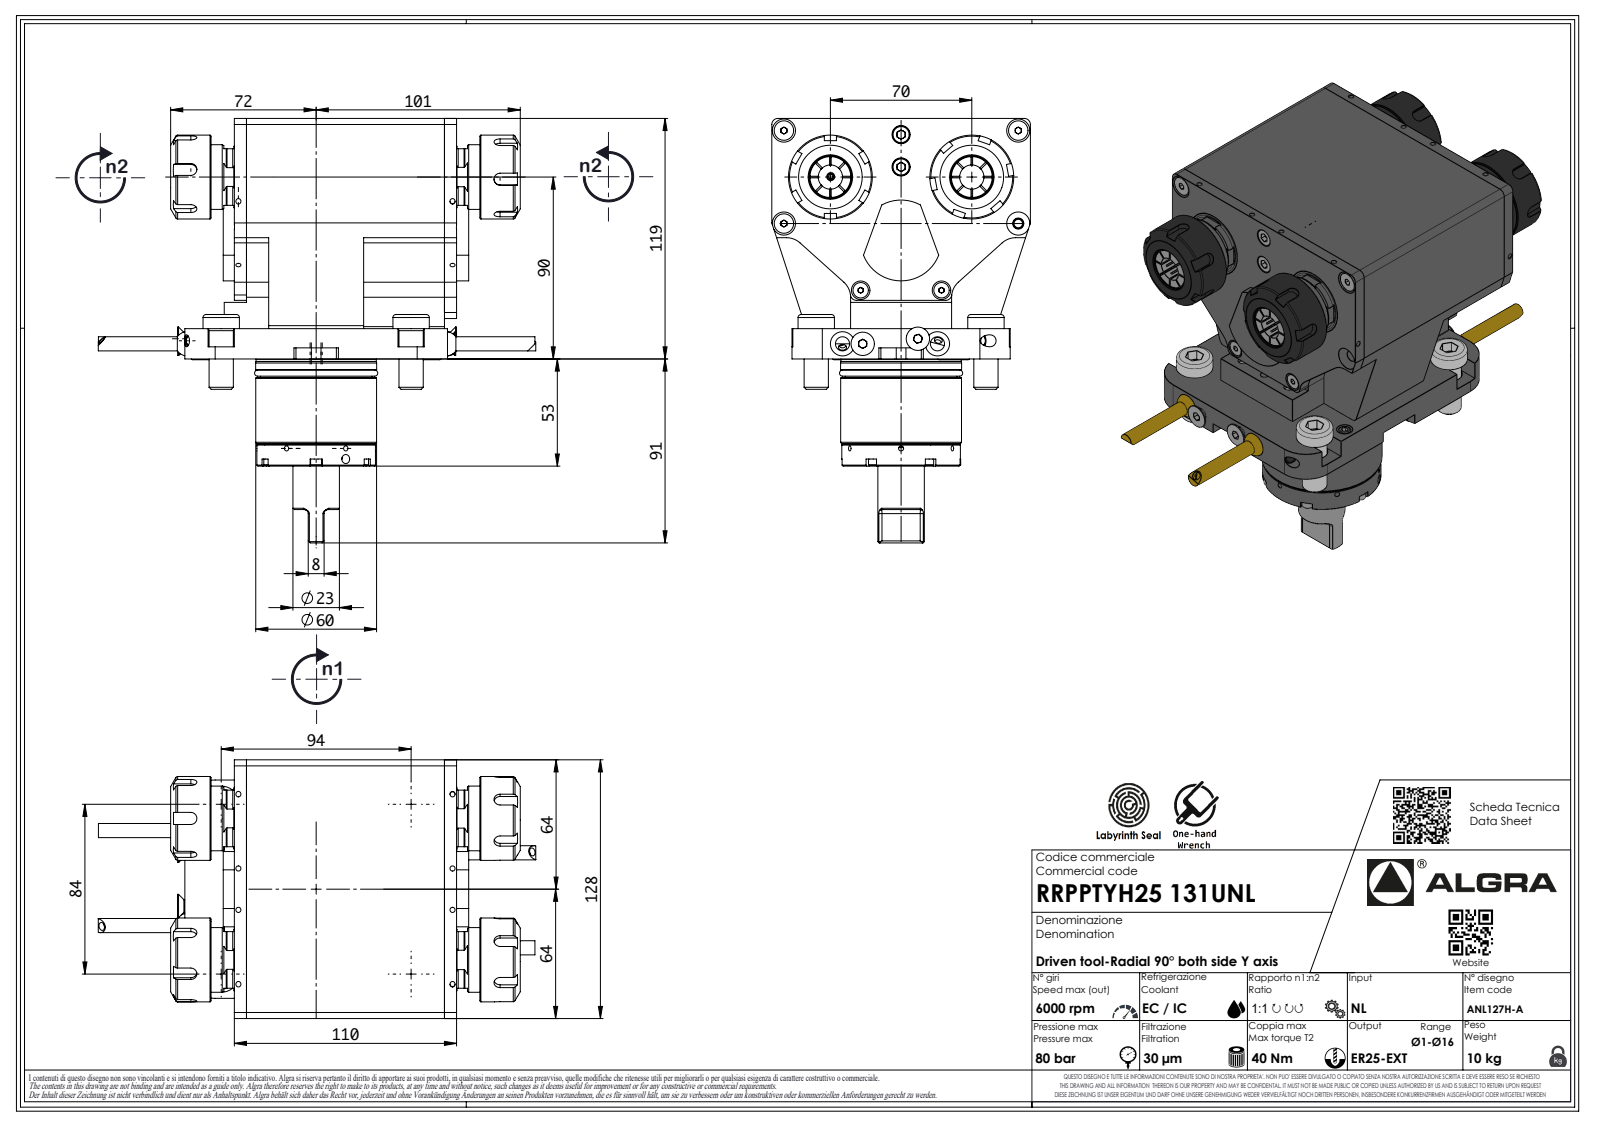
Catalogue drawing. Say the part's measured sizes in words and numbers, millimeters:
The part is named "RRPPTYH25131UNL". Its 3-D file was written by "SolidWorks 2023 (AUTOMOTIVE_DESIGN)". It is 5 solids with 980 faces: 579 planar, 215 cylindrical and 186 other. Overall it measures 218.3 by 210 by 128 millimeters. Its volume is 1 763 000 cubic millimeters and its surface area 154 473 square millimeters. Round holes: 4 of diameter 4, 4 of diameter 13, 2 of diameter 6.8, 1 of diameter 3.15, 1 of diameter 5, 1 of diameter 37.2, 1 of diameter 41.2, 1 of diameter 45.2, 1 of diameter 49.2. Round bosses or shafts: 4 of diameter 12, 4 of diameter 7, 3 of diameter 11.57, 3 of diameter 6, 2 of diameter 41.5, 2 of diameter 32, 1 of diameter 59.9, 1 of diameter 59.8. Partial cylindrical surfaces (rounded edges, fillets, slot ends): 30 of radius 3, 16 of radius 6.75, 16 of radius 8, 10 of radius 2, 7 of radius 0.5, 7 of radius 0.78, 7 of radius 5.55, 4 of radius 10. The main face-to-face distances are 119, 110, 15, 104, 128, 5.5, 17, 31.53, 141.53, 22.5. The hole center spacings are 17.46, 68.36, 84, 94, 102.26, 121.76, 126.06, 81.15.
